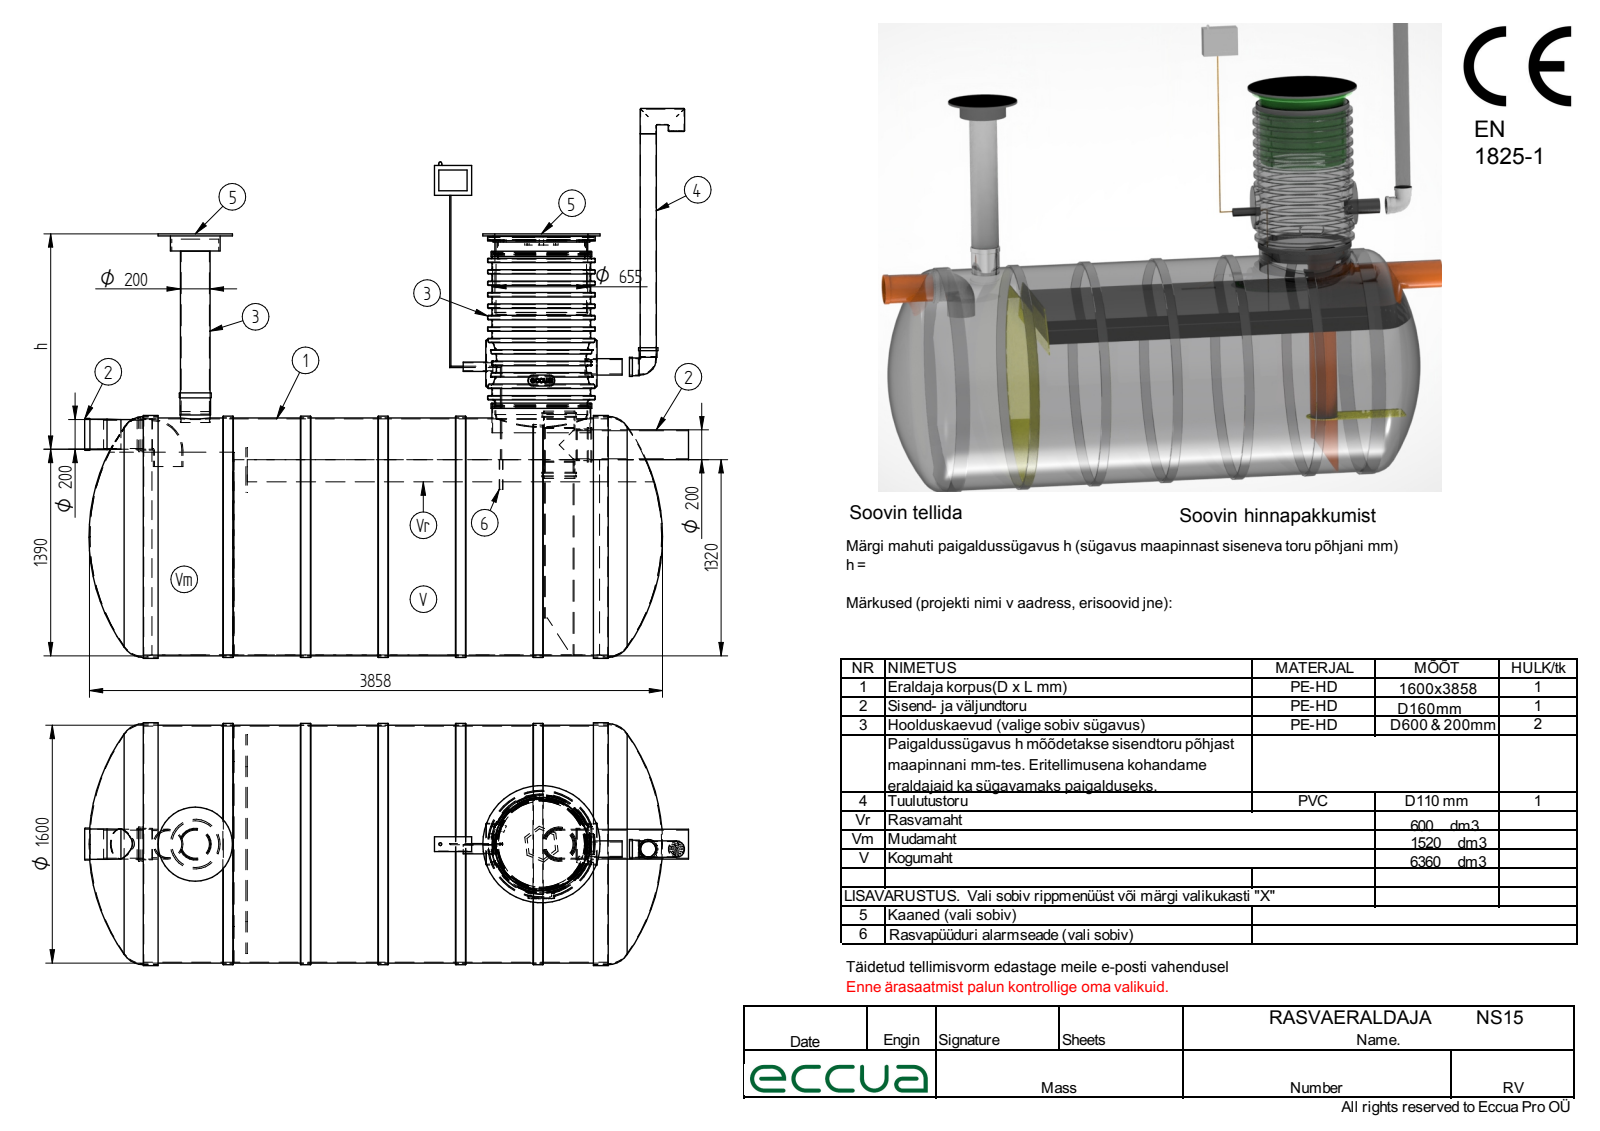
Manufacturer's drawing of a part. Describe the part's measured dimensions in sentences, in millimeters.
The part is named "Rasvaeraldaja NS15; 2260.013; Polv D200; 2260.002 (+8 more)". Its 3-D file was written by "Solid Edge (AUTOMOTIVE_DESIGN)". It is 42 solids with 791 faces: 309 planar, 268 cylindrical and 214 other. Overall it measures 4160.41 by 4064 by 2555.02 millimeters. Its volume is 29 370 000 000 cubic millimeters and its surface area 190 200 000 square millimeters. Round holes: 31 of diameter 10, 5 of diameter 200, 3 of diameter 103.2, 2 of diameter 100, 2 of diameter 188, 2 of diameter 190, 2 of diameter 220, 1 of diameter 6, 1 of diameter 20.4, 1 of diameter 53.6, 1 of diameter 96.8, 1 of diameter 105. Round bosses or shafts: 4 of diameter 110, 3 of diameter 212, 3 of diameter 8.5, 2 of diameter 232, 2 of diameter 215, 2 of diameter 205, 2 of diameter 130, 2 of diameter 120. Partial cylindrical surfaces (rounded edges, fillets, slot ends): 4 of radius 3, 4 of radius 5, 4 of radius 30, 4 of radius 35, 2 of radius 135, 2 of radius 140, 1 of radius 130, 1 of radius 289.9. The main face-to-face distances are 8, 150, 88, 5, 50, 200, 1469.57, 1519.57, 1669.57, 96. The hole center spacings are 72.08, 17.8, 34.71, 40, 49.88, 62.55, 26.75, 77.99.
